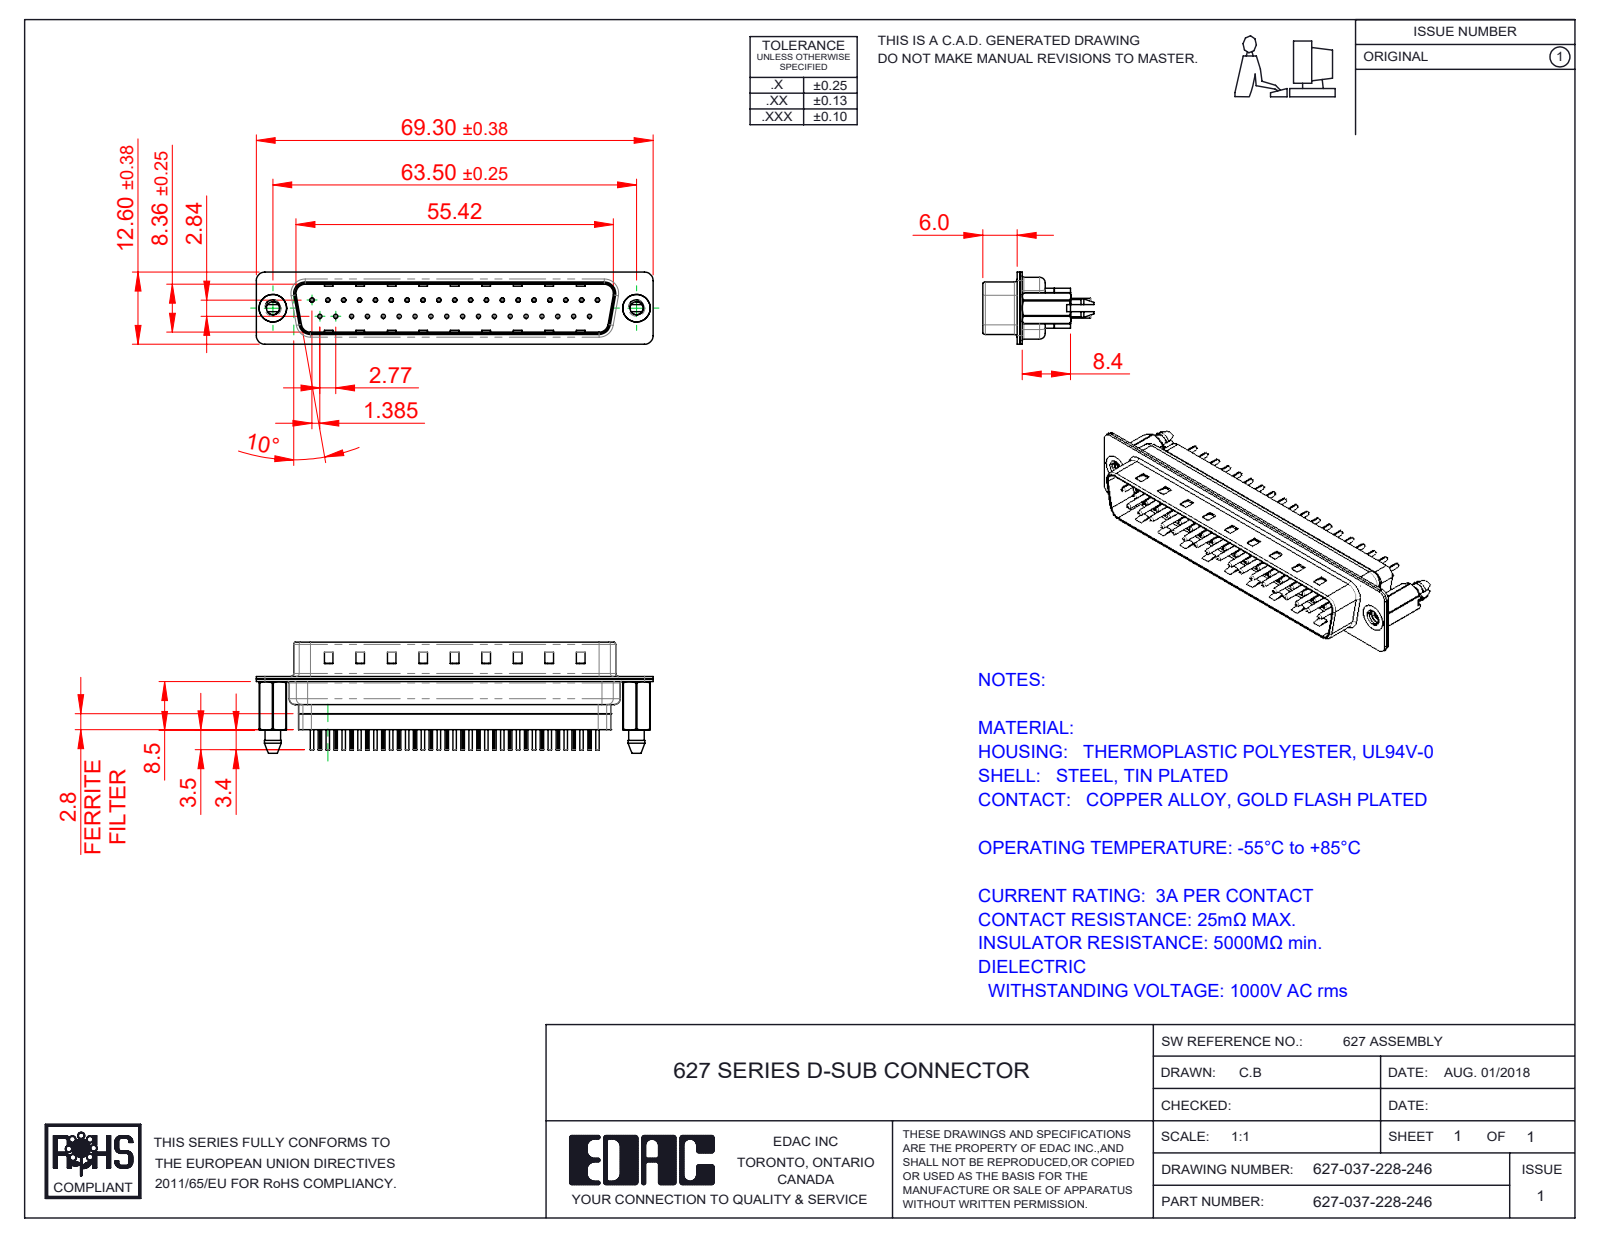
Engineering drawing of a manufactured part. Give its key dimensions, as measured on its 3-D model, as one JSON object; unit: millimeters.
{"part_name": "627 Contact Row 1_28L; 627 Housing_37 FF; 627-037-228-046; 627 4-40 Threaded Boardlock_FF (+3 more)", "step_written_by": "SolidWorks 2020 (CONFIG_CONTROL_DESIGN)", "units": "millimeters", "bodies": {"solids": 43, "faces": 4279, "planar": 1129, "cylindrical": 1655, "other": 1495}, "overall_size": [69.3, 19.4, 12.6], "volume_mm3": 4738, "surface_area_mm2": 12761, "round_holes": [[0.2, 37], [0.35, 37], [1.1, 37], [1.6, 37], [2.26, 2], [4, 2], [4.8, 2]], "round_bosses_or_shafts": [[2, 37], [1.5, 37], [0.75, 37], [0.6, 37], [4.9, 2]], "partial_cylinders_radius": [[0.1, 74], [1.5, 18], [2, 12], [1.6, 10], [0.5, 8], [0.25, 4], [0.6, 4], [0.65, 4]], "face_to_face_distances": [0.4, 6.05, 0.82, 9.58, 0.45, 0.68, 7.68, 8.4, 1.5, 1.08], "hole_center_spacings": [3.16, 2.77, 5.54, 8.31, 5.04, 10.1, 11.08, 12.78]}
